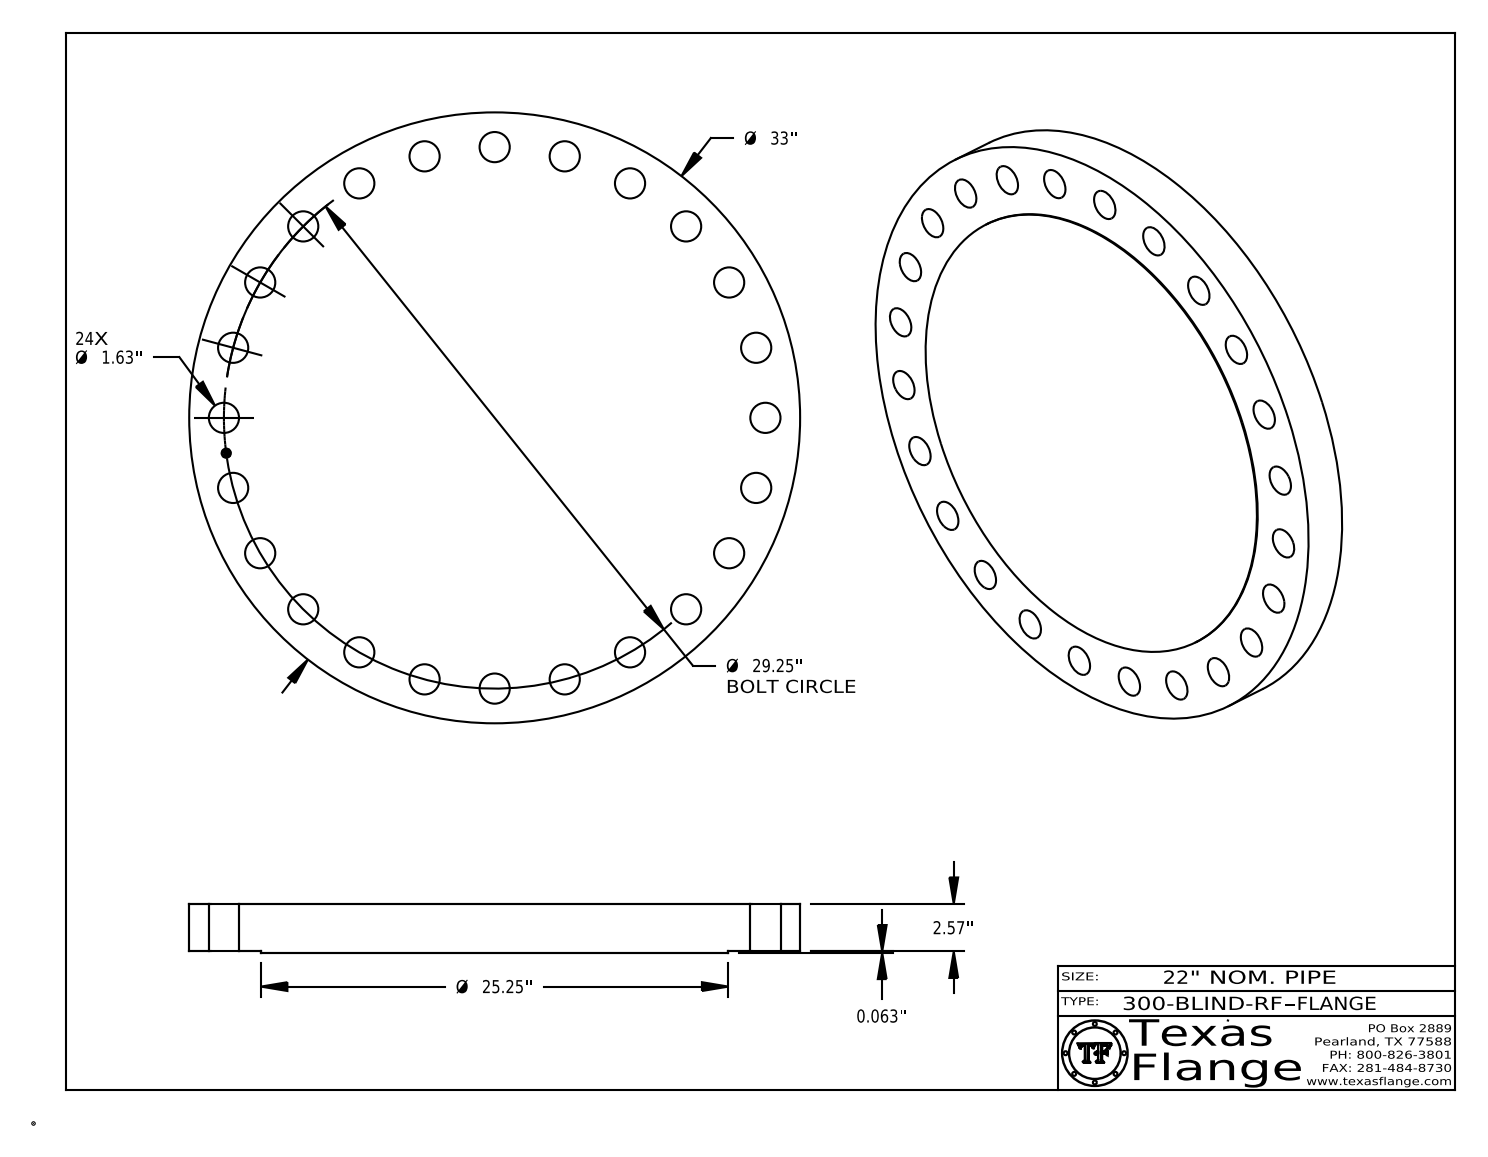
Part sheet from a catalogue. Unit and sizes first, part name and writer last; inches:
Units: inches
Overall size (bounding box): 33 × 33 × 2.633
Round holes (diameter × count): ⌀1.63 ×24, ⌀0.495 ×1
Round bosses / shafts (diameter × count): ⌀0.03 ×8, ⌀33 ×1, ⌀25.25 ×1, ⌀0.39 ×1
Main face-to-face distances: 2.633, 0.063, 2.57, 2.618, 2.555, 0.015, 0.148, 0.145, 0.027, 0.096
Hole centre spacings: 27.024, 7.57, 20.683, 3.818, 11.194, 17.806, 23.206, 28.254
Volume: 2 101 in³ · Surface area: 2 198 in²
Bodies: 1 solid, 440 faces (368 planar, 72 cylindrical, 0 other)
Part name (STEP PRODUCT): 300-BLIND-RF
STEP written by: CATIA V5 STEP AP214 (AUTOMOTIVE_DESIGN)
